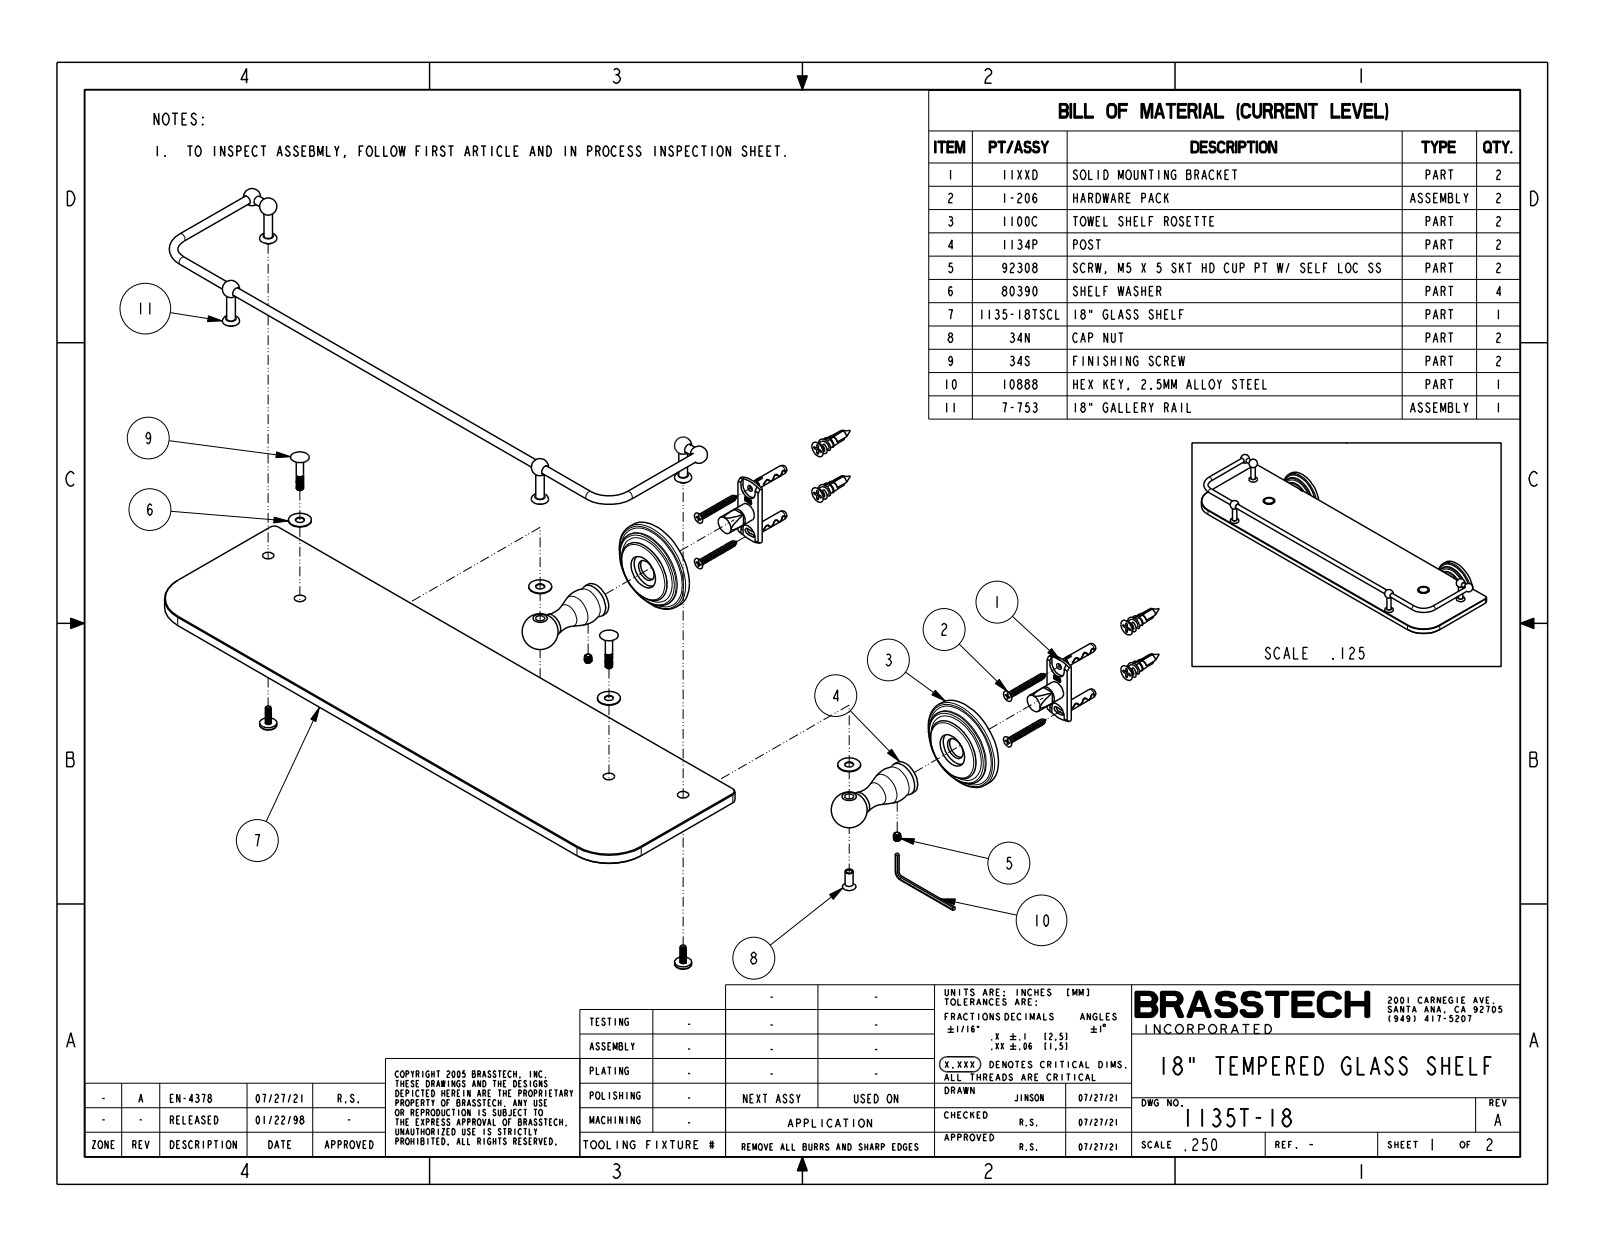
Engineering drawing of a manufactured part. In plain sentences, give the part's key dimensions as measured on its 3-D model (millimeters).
The part is named "1135T-18". Its 3-D file was written by "CREO PARAMETRIC BY PTC INC, 2018400 (CONFIG_CONTROL_DESIGN)". It is 1 solid with 390 faces: 54 planar, 164 cylindrical and 172 other. Overall it measures 457.2 by 141.6 by 85.9 millimeters. Its volume is 587 300 cubic millimeters and its surface area 165 900 square millimeters. Round holes: 3 of diameter 2.5, 2 of diameter 3.5, 1 of diameter 3.5, 1 of diameter 5, 1 of diameter 6.5, 1 of diameter 6.6, 1 of diameter 6.9. Round bosses or shafts: 7 of diameter 6, 2 of diameter 65, 2 of diameter 55.4, 2 of diameter 44.4, 2 of diameter 16, 2 of diameter 5.7, 1 of diameter 6.2, 1 of diameter 5.9. Partial cylindrical surfaces (rounded edges, fillets, slot ends): 2 of radius 5, 2 of radius 31.8, 1 of radius 3.3. The main face-to-face distances are 7.9, 14.6, 141.6, 127, 13, 1.6, 128.6, 9.2, 3.8, 5.4. The hole center spacings are 89, 304.8.
